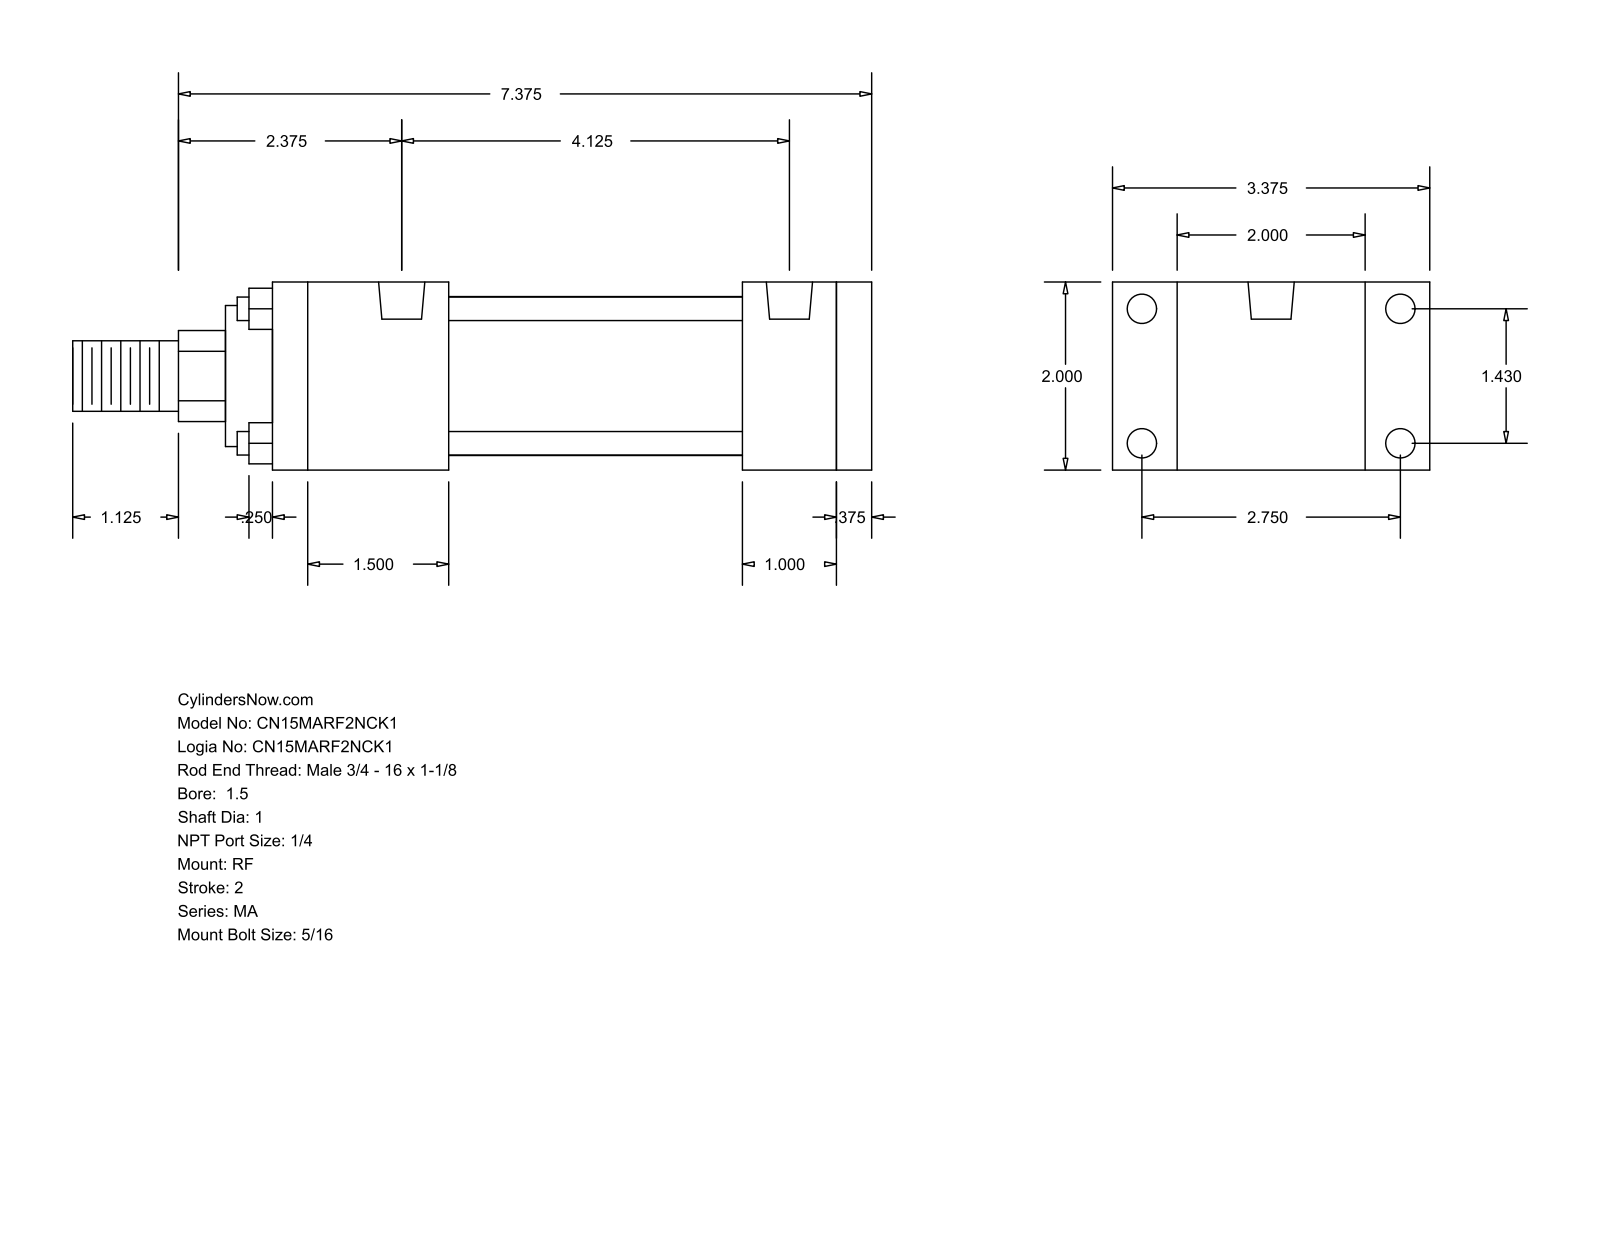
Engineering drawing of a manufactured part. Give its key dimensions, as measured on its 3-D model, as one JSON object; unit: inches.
{"part_name": "MA_RF__0150_1", "step_written_by": "GSSL Pune (CONFIG_CONTROL_DESIGN)", "units": "inches", "bodies": {"solids": 0, "faces": 92, "planar": 64, "cylindrical": 28, "other": 0}, "overall_size": [8.5, 3.375, 2], "round_holes": [[0.313, 8], [0.492, 2]], "round_bosses_or_shafts": [[0.25, 4], [1.69, 1], [1.5, 1], [1, 1], [0.75, 1]], "partial_cylinders_radius": [[0.484, 1]], "face_to_face_distances": [2, 0.375, 6.375, 6, 1, 5, 1.375, 1.875, 3.125, 4.125], "hole_center_spacings": [1.43, 2.75, 3.099, 4.125]}
